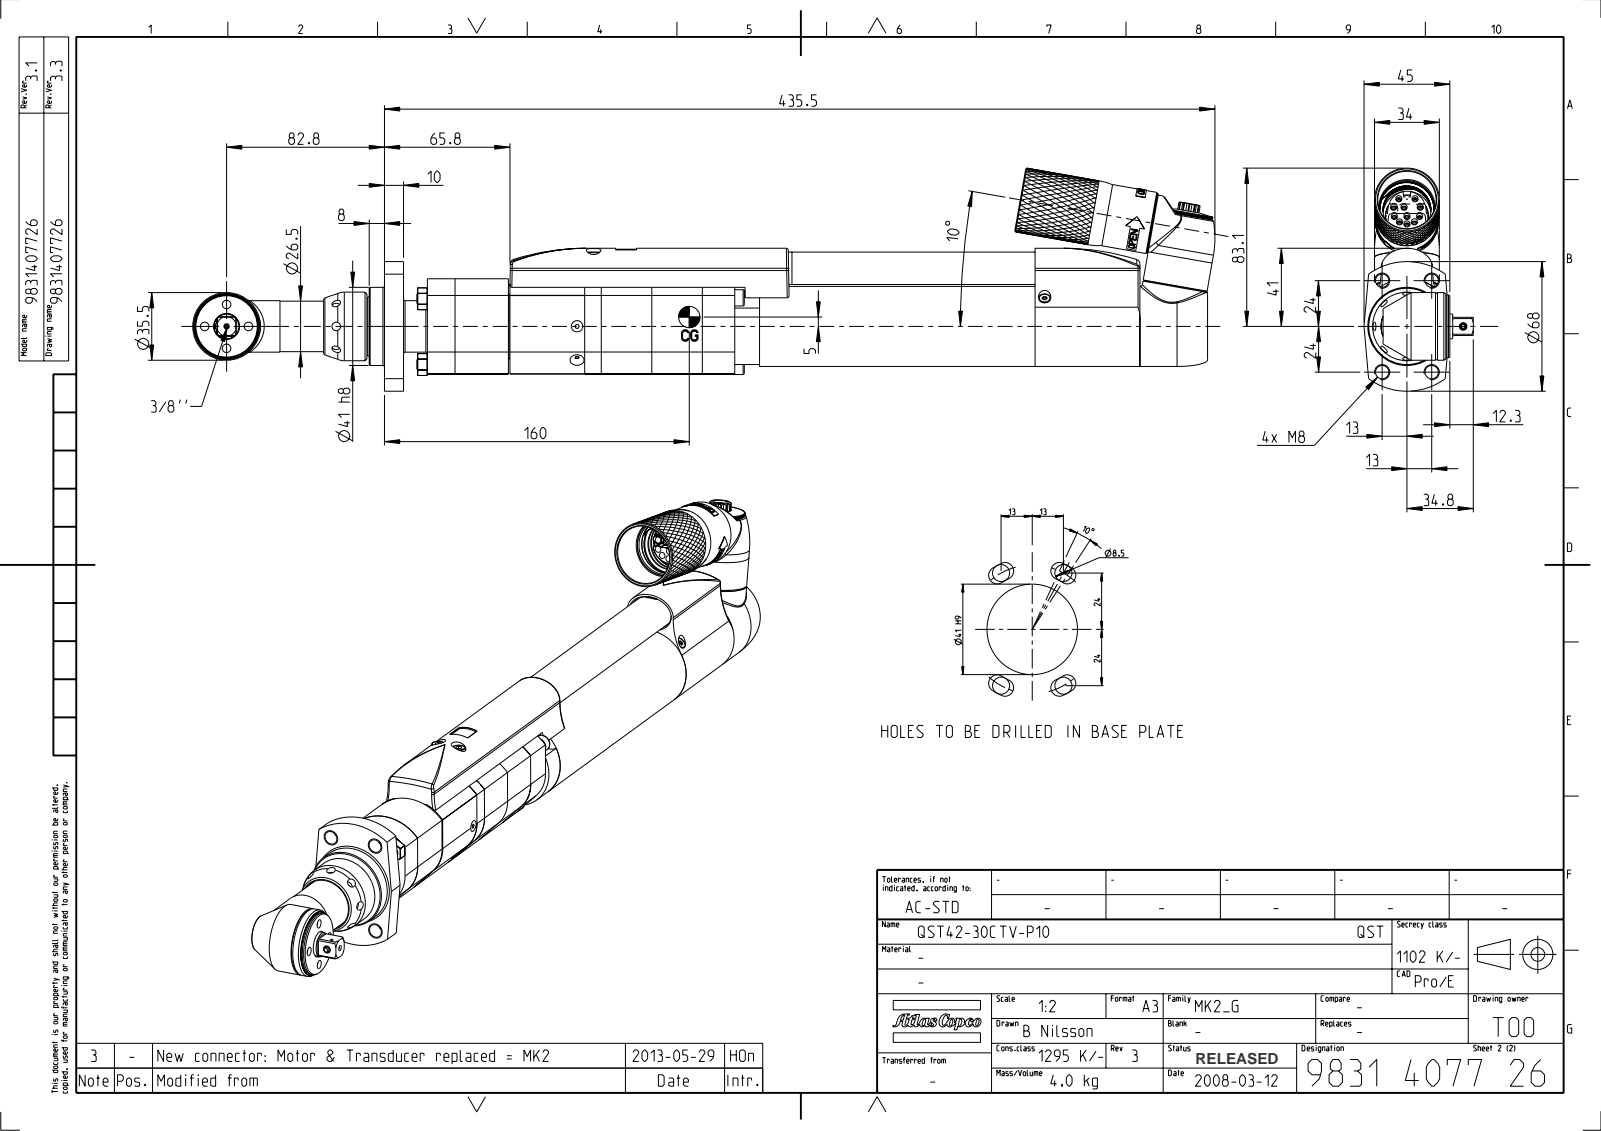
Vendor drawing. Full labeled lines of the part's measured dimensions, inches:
Part name (STEP PRODUCT): 4230260102; 4230260112_ASM; 4230262500; 0219110017 (+8 more)
STEP written by: PRO/ENGINEER BY PARAMETRIC TECHNOLOGY CORPORATION, 2012420 (CONFIG_CONTROL_DESIGN)
Units: inches
Bodies: 44 solids, 5060 faces (2023 planar, 1649 cylindrical, 1388 other)
Overall size (bounding box): 21.105 × 4.609 × 2.256
Volume: 27.96 in³ · Surface area: 431 in²
Round holes (diameter × count): ⌀0.104 ×11, ⌀0.129 ×11, ⌀0.142 ×11, ⌀0.177 ×10, ⌀0.13 ×7, ⌀0.097 ×5, ⌀0.128 ×5, ⌀0.276 ×5, ⌀0.315 ×5, ⌀0.055 ×3, ⌀0.059 ×3, ⌀0.116 ×3
Round bosses / shafts (diameter × count): ⌀0.236 ×7, ⌀0.118 ×7, ⌀1.339 ×6, ⌀0.157 ×5, ⌀0.197 ×4, ⌀1.181 ×3, ⌀0.335 ×3, ⌀0.098 ×3
Partial cylindrical surfaces — rounded edges, fillets, slot ends (radius × count): R0.039 ×79, R0.008 ×70, R0.004 ×53, R0.02 ×21, R0.011 ×12, R0.02 ×12, R0.079 ×9, R0.207 ×4
Main face-to-face distances: 1.496, 1.043, 0.138, 1.063, 0.394, 7.35, 0.886, 0.492, 4.476, 1.634
Hole centre spacings: 0.282, 0.292, 0.627, 0.289, 0.591, 0.292, 0.293, 0.363
